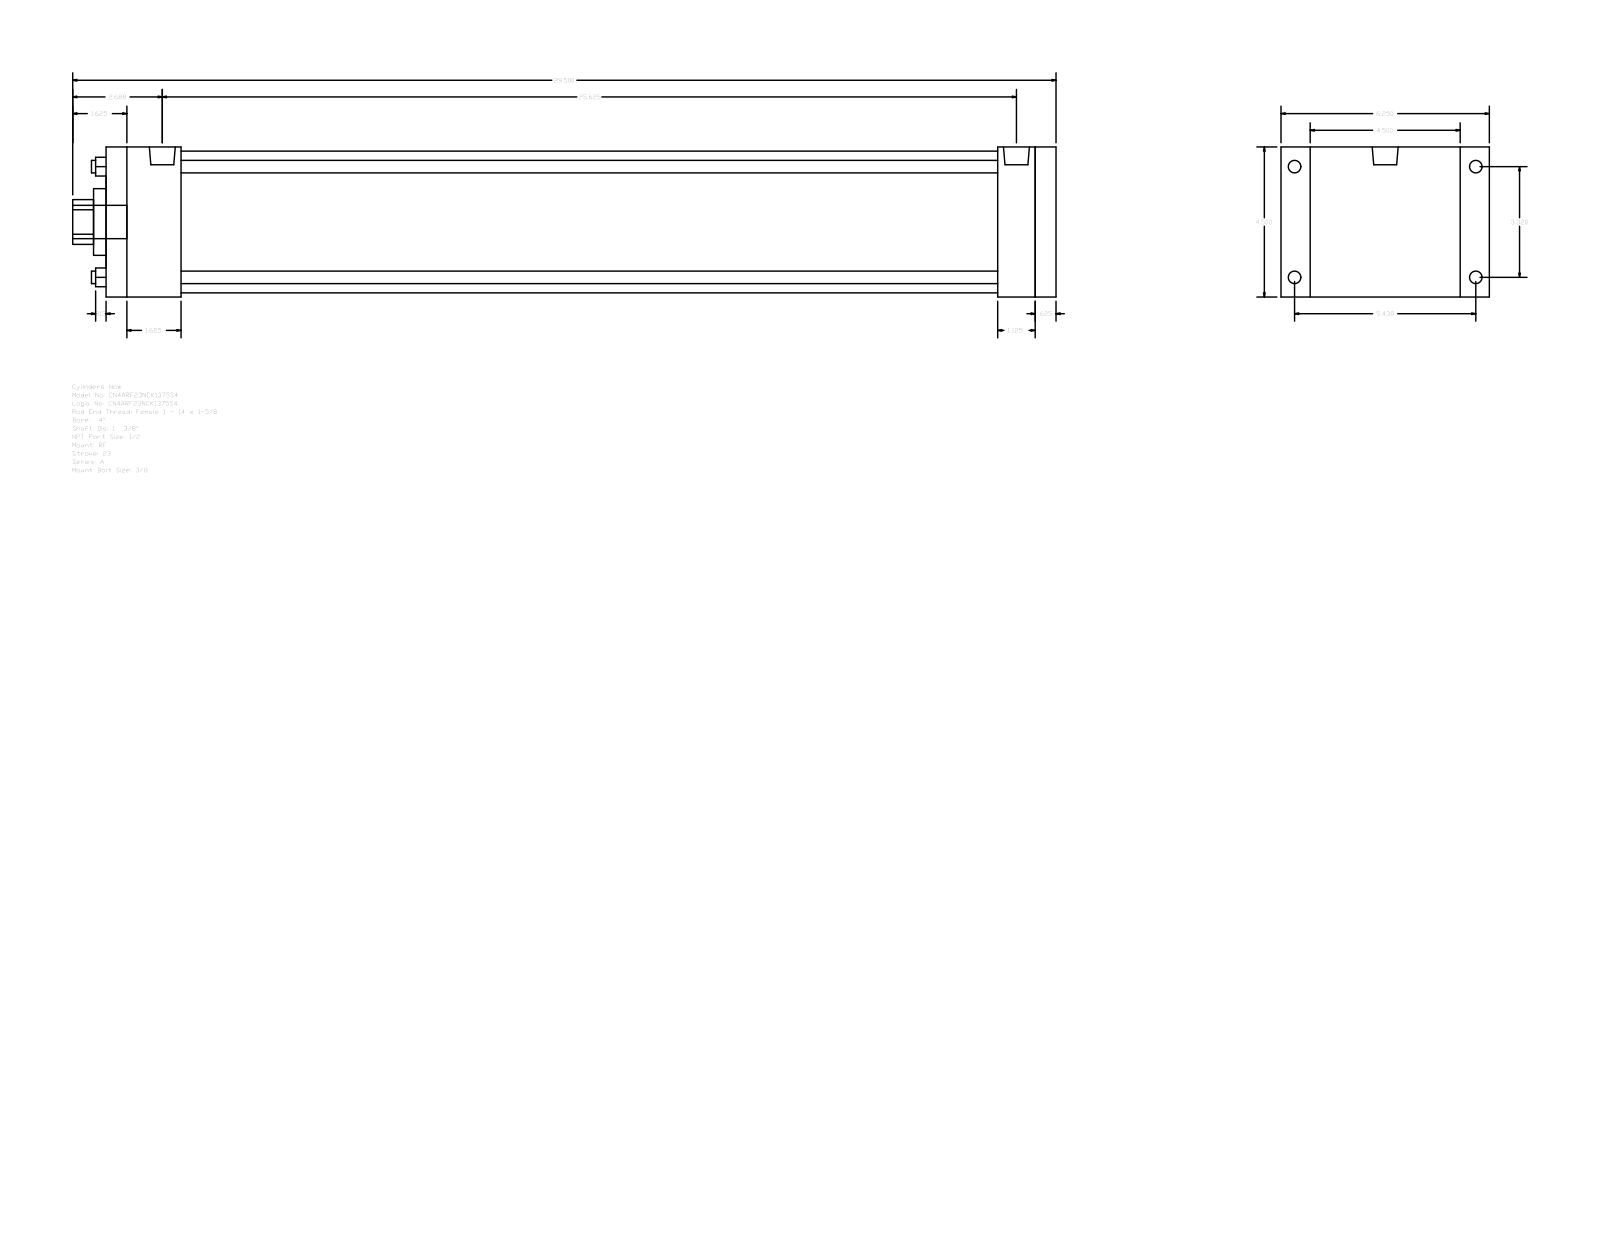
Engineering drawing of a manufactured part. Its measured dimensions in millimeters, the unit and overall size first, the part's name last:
Units: millimetres
Overall size (bounding box): 749.3 × 158.75 × 114.3
Round holes (diameter × count): ⌀9.53 ×4, ⌀34.92 ×1, ⌀50.8 ×1, ⌀107.95 ×1
Round bosses / shafts (diameter × count): ⌀9.53 ×4, ⌀8.73 ×4, ⌀19.77 ×2, ⌀25.4 ×1
Partial cylindrical surfaces — rounded edges, fillets, slot ends (radius × count): R17.06 ×1
Main face-to-face distances: 114.3, 723.9, 15.88, 708.02, 28.57, 22.23, 136.53, 679.45, 44.45, 57.15
Hole centre spacings: 59.62, 84.32, 119.25
Bodies: 0 solids, 92 faces (64 planar, 28 cylindrical, 0 other)
Part name (STEP PRODUCT): A_RF__0400_1.375
STEP written by: GSSL Pune (CONFIG_CONTROL_DESIGN)
